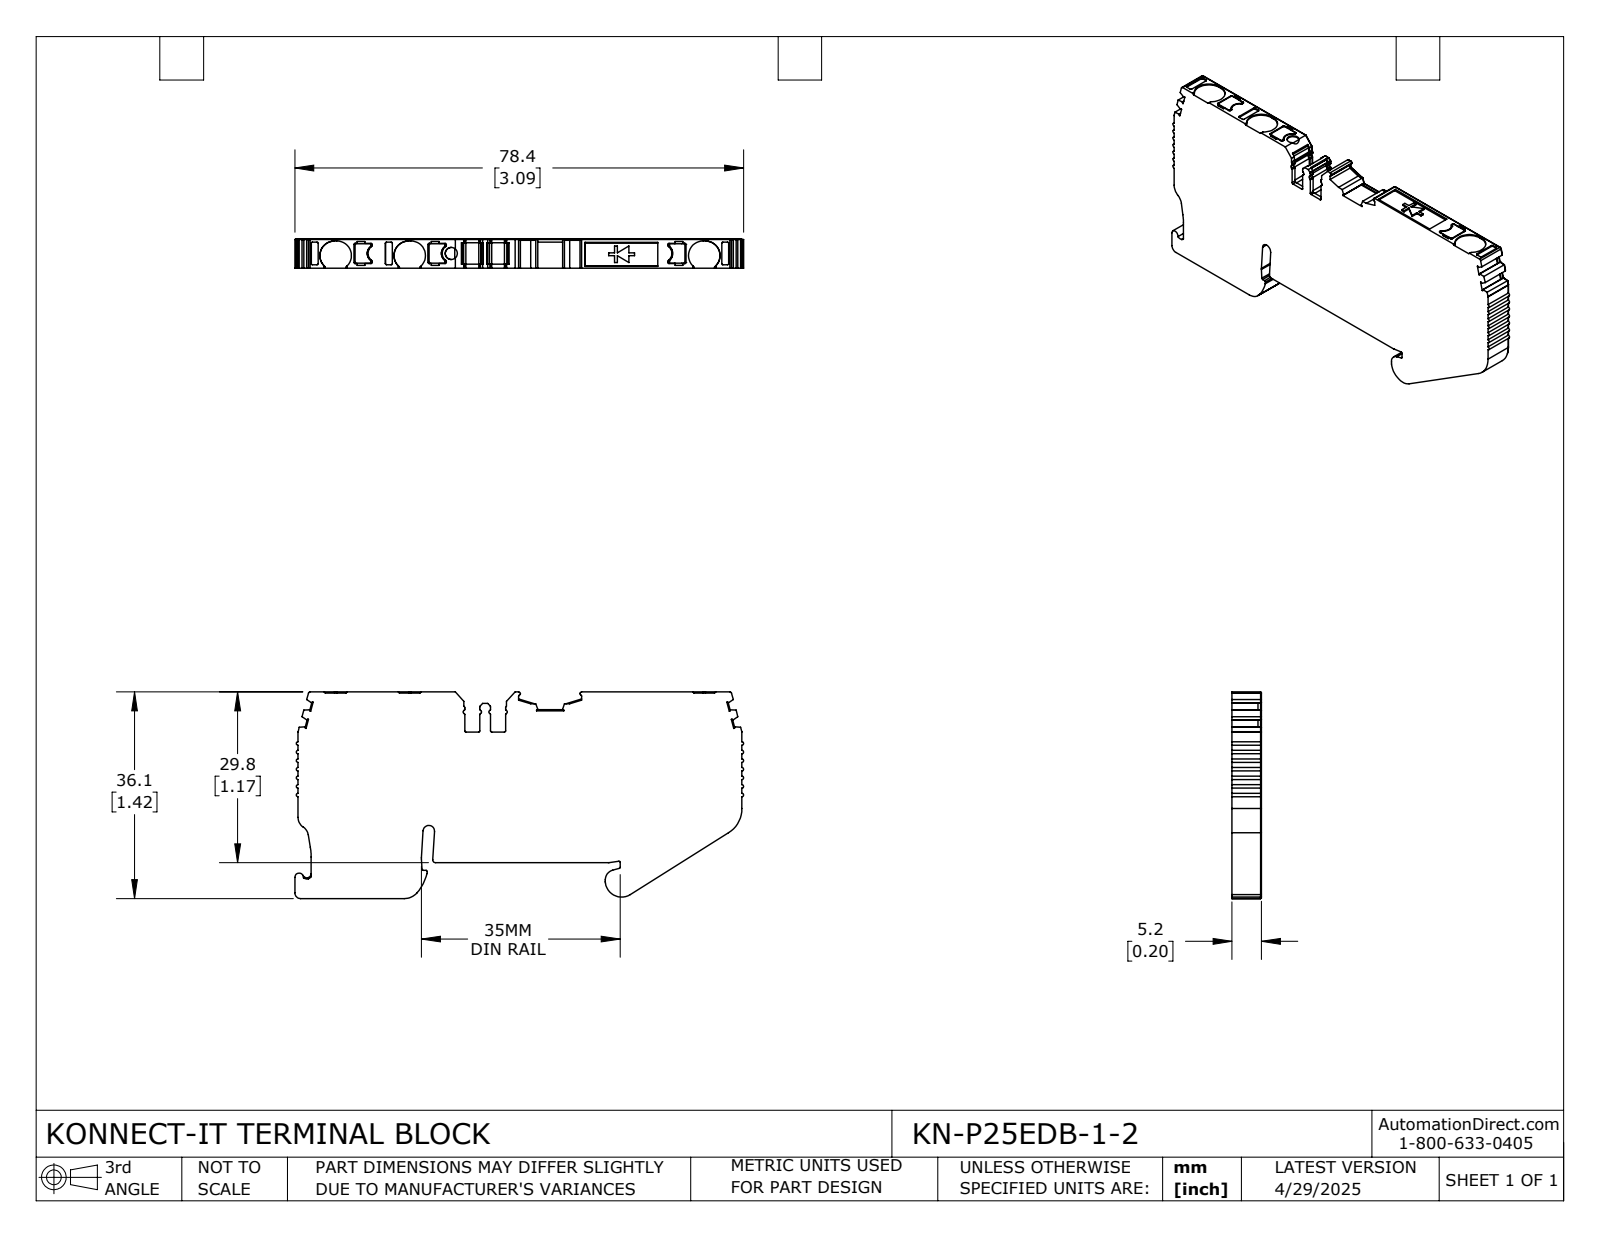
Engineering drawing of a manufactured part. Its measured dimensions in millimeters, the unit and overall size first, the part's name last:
Units: millimetres
Overall size (bounding box): 78.36 × 36.07 × 5.15
Round holes (diameter × count): ⌀2.1 ×1
Partial cylindrical surfaces — rounded edges, fillets, slot ends (radius × count): R0.2 ×66, R0.3 ×39, R0.5 ×16, R0.1 ×13, R0.15 ×12, R0.4 ×9, R2.55 ×6, R1 ×3
Main face-to-face distances: 5.15, 29.61, 29.81, 6.26, 35.87, 36.07, 77.52, 1.2, 5, 4.5
Volume: 11 973 mm³ · Surface area: 6 212 mm²
Bodies: 1 solid, 595 faces (341 planar, 251 cylindrical, 3 other)
Part name (STEP PRODUCT): KN-P25EDB-1-2
STEP written by: SolidWorks 2024 (CONFIG_CONTROL_DESIGN)
